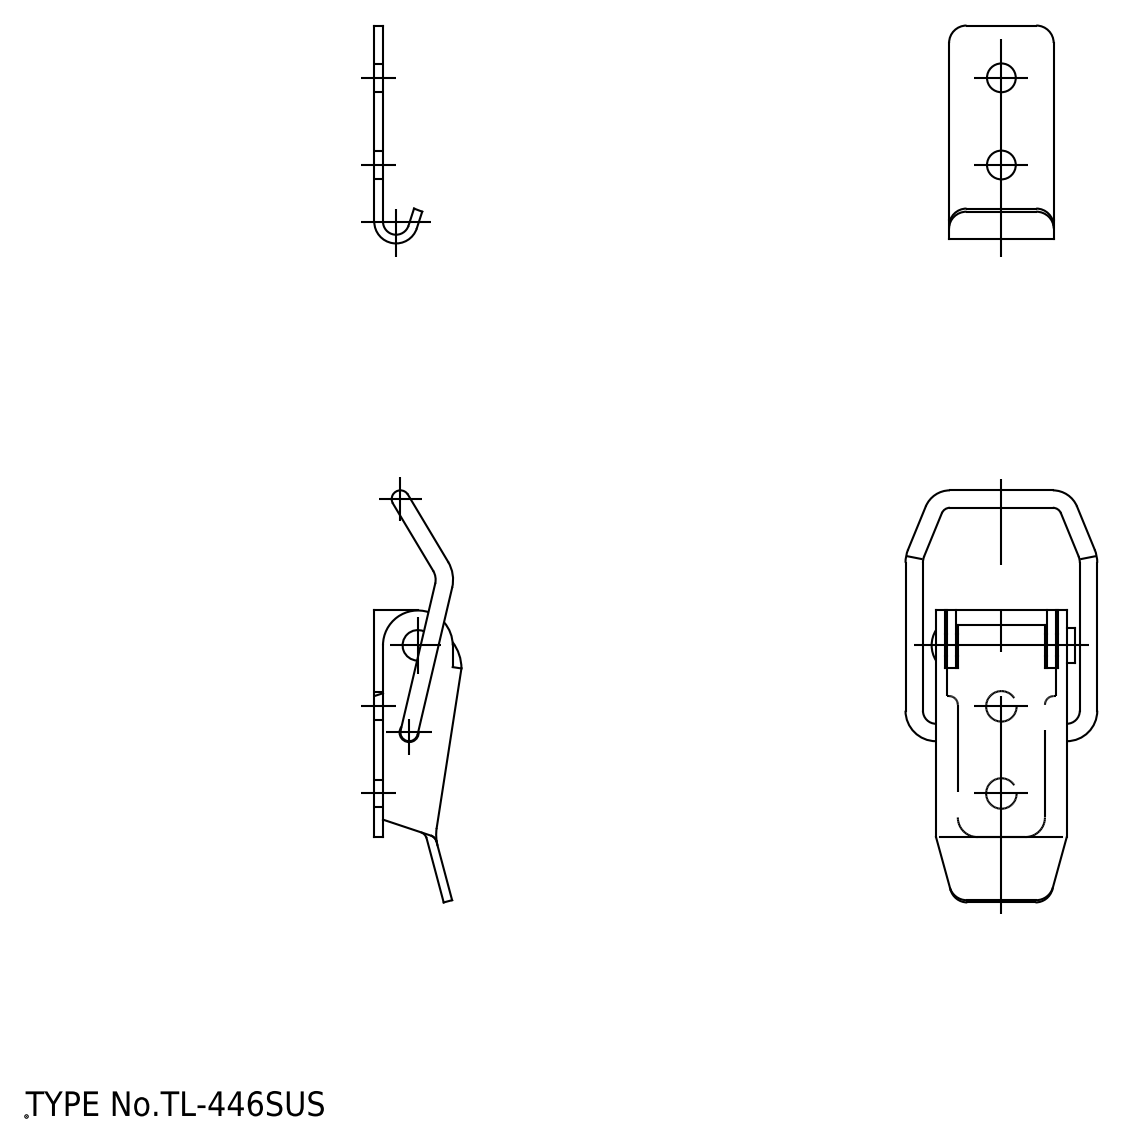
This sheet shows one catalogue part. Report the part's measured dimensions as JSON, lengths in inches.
{"part_name": "ベース; レバー; アーム; TL_446SUS_K", "step_written_by": "spGate 20.6.3 (****-****-****-****) (AUTOMOTIVE_DESIGN)", "units": "inches", "bodies": {"solids": 4, "faces": 125, "planar": 49, "cylindrical": 59, "other": 17}, "overall_size": [2.697, 0.866, 0.398], "volume_in3": 0.112, "surface_area_in2": 6.229, "round_holes": [[0.138, 3], [0.13, 2], [0.087, 1]], "round_bosses_or_shafts": [[0.079, 5], [0.157, 1], [0.098, 1]], "partial_cylinders_radius": [[0.039, 8], [0.079, 6], [0.089, 2], [0.157, 2], [0.02, 1], [0.059, 1], [0.098, 1], [0.118, 1]], "face_to_face_distances": [0.039, 0.551, 0.049, 0.502, 0.591, 0.512, 0.492, 0.453, 0.541, 0.089], "hole_center_spacings": [0.394, 1.575, 0.396, 1.181, 1.969]}
